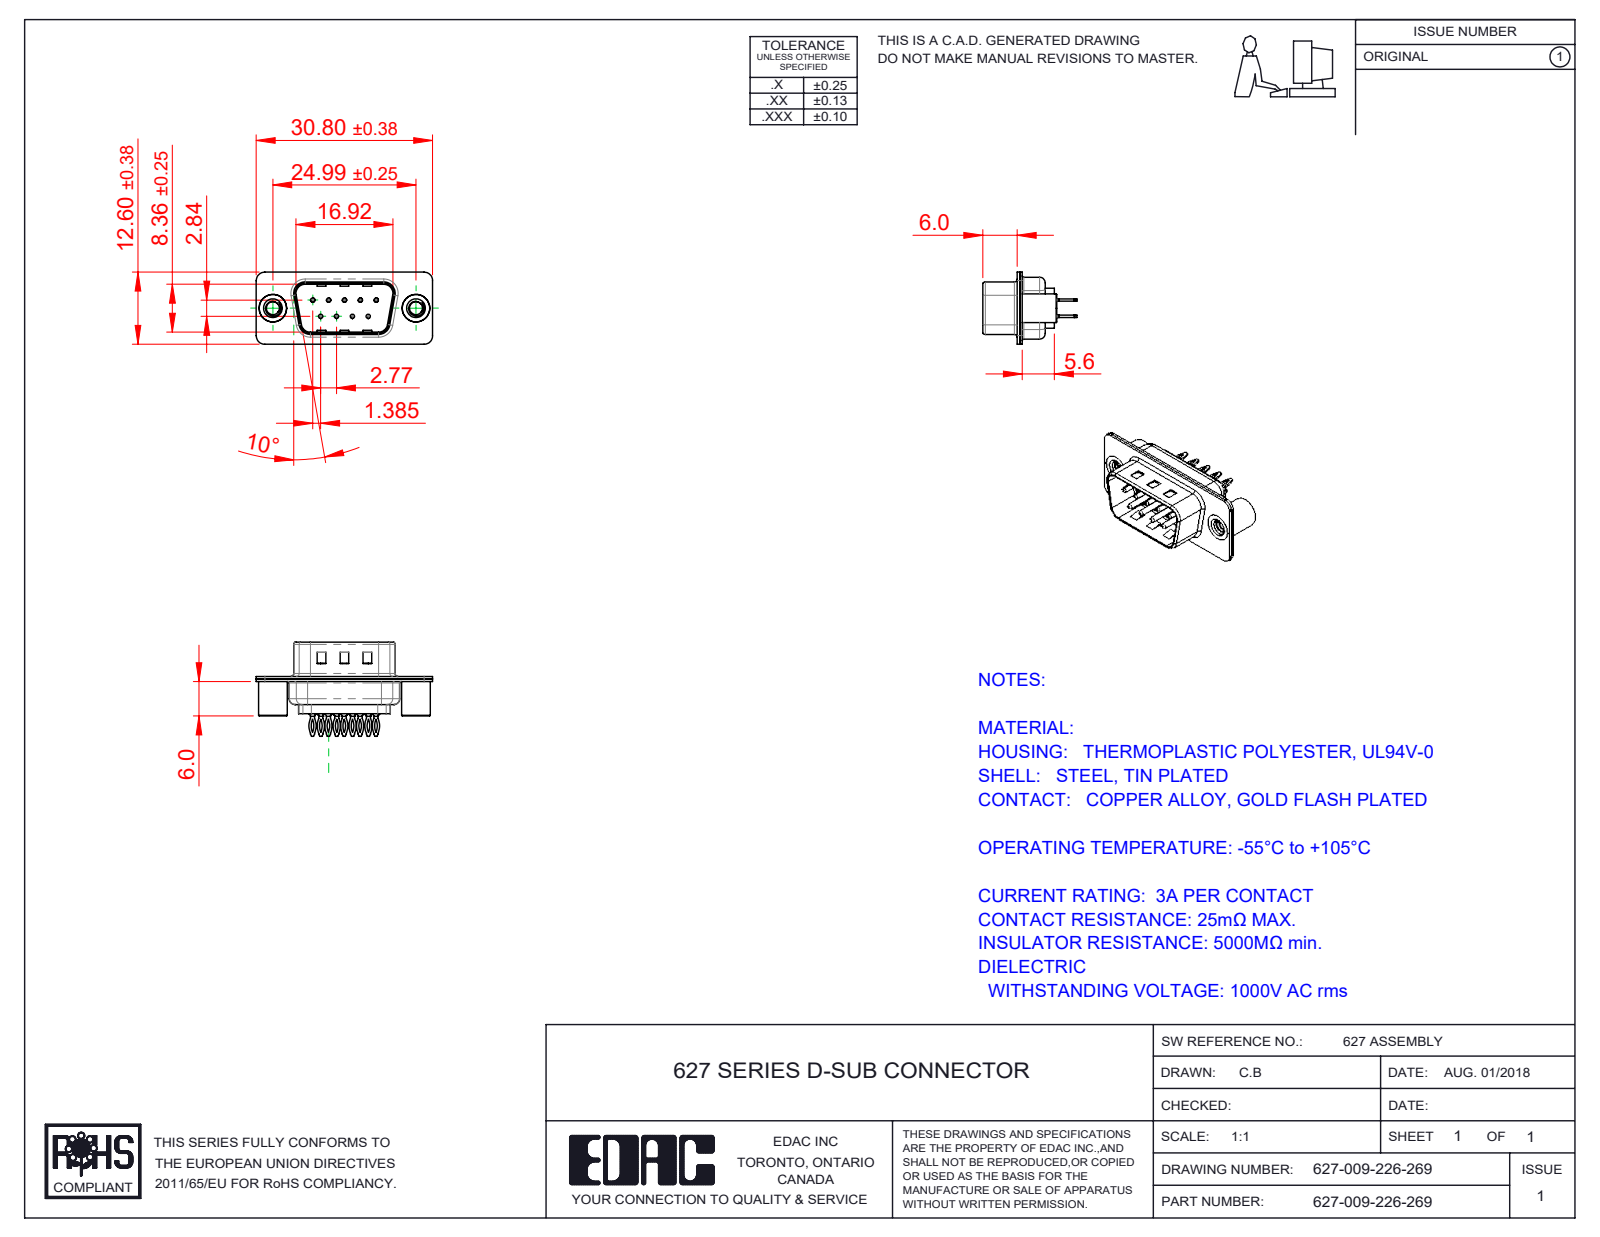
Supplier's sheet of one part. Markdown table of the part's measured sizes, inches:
| quantity | value |
| --- | --- |
| part name | 627-009-226-069; 627 Contact Row 1_26L; 627 Shell Front_09 Contacts; 627 Shell Rear_09 Contacts (+3 more) |
| STEP written by | SolidWorks 2020 (CONFIG_CONTROL_DESIGN) |
| units | inches |
| bodies | 14 solids, 1010 faces (287 planar, 428 cylindrical, 295 other) |
| overall size | 1.213 × 0.648 × 0.496 |
| volume | 0.086 in³ |
| surface area | 6.349 in² |
| round holes (diameter × count) | 0.014 × 9, 0.043 × 9, 0.063 × 9, 0.089 × 2, 0.157 × 2, 0.189 × 2 |
| round bosses / shafts (diameter × count) | 0.079 × 9, 0.059 × 9, 0.03 × 9, 0.197 × 2, 0.193 × 2 |
| partial cylindrical surfaces (radius × count) | 0.059 × 18, 0.115 × 18, 0.131 × 18, 0.079 × 12, 0.02 × 8, 0.063 × 8, 0.01 × 4, 0.024 × 4 |
| main face-to-face distances | 0.016, 0.018, 0.035, 0.032, 0.377, 0.055, 0.345, 0.256, 0.02, 0.059 |
| hole center spacings | 0.124, 0.109, 0.218, 0.198, 0.198, 0.327, 0.294, 0.295 |
